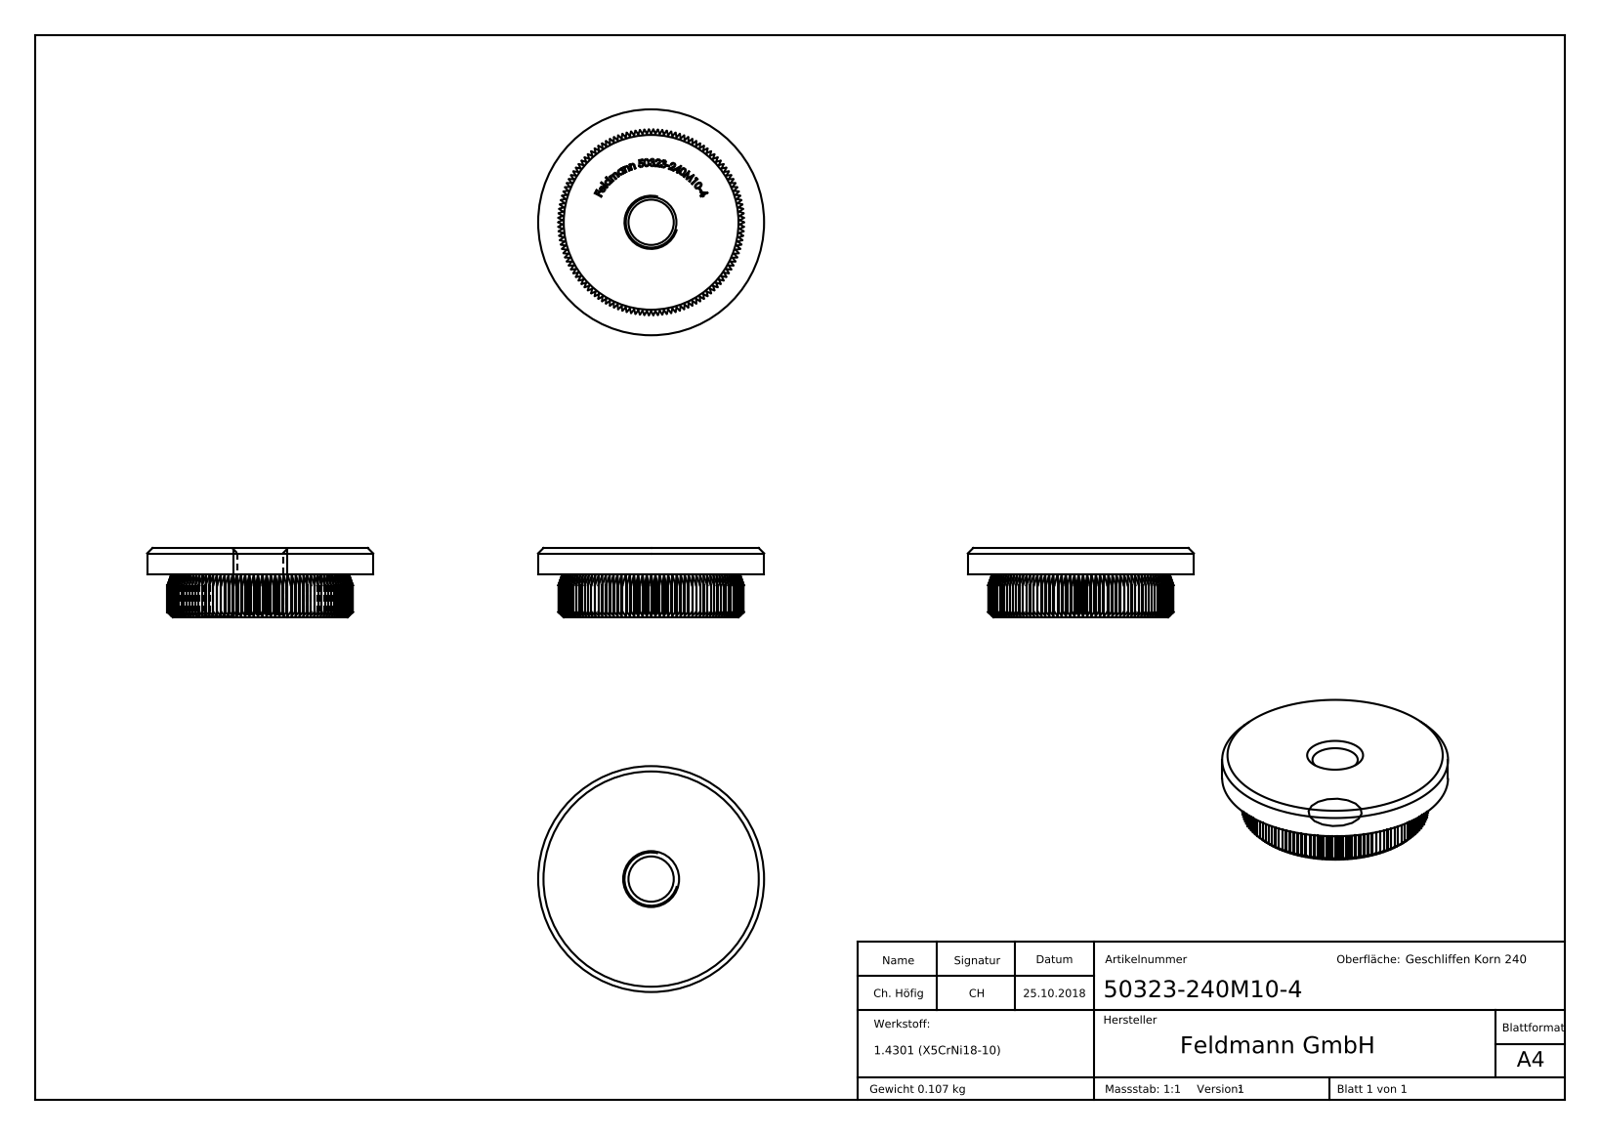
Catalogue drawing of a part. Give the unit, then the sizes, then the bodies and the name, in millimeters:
Units: millimetres
Overall size (bounding box): 42.4 × 42.4 × 13
Round holes (diameter × count): ⌀8.5 ×1
Round bosses / shafts (diameter × count): ⌀42.4 ×1
Partial cylindrical surfaces — rounded edges, fillets, slot ends (radius × count): R17.4 ×1
Main face-to-face distances: 13, 8, 5, 16.7, 16.72, 16.68, 7.9, 12.9, 0.54, 0.67
Volume: 13 502 mm³ · Surface area: 5 169 mm²
Bodies: 1 solid, 821 faces (410 planar, 134 cylindrical, 277 other)
Part name (STEP PRODUCT): 50323-240M10-4
STEP written by: SolidWorks 2015 (CONFIG_CONTROL_DESIGN)
